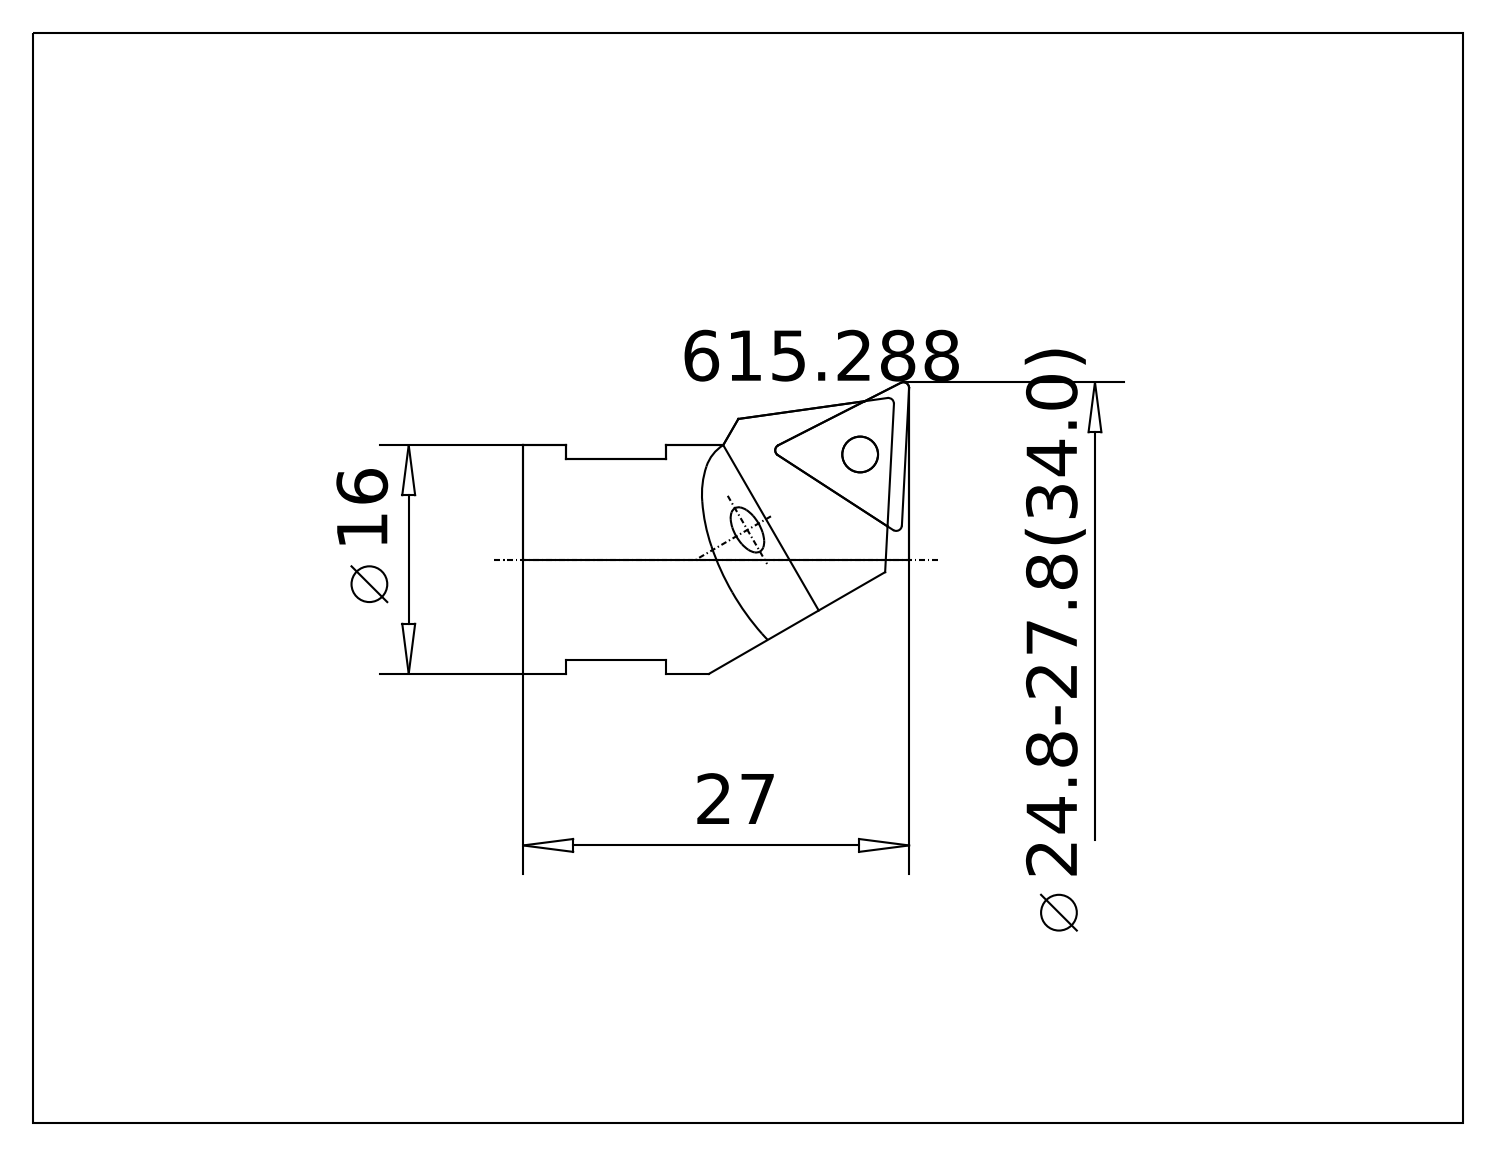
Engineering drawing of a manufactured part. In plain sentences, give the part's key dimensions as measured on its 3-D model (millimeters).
The part is named "615.288 Kaiser E25 TC11|655.383 Kaiser TCGT 110204 K10C;Kombinieren1; 615.288 Kaiser E25 TC11|694.122 Kaiser ETL M2.5x6.5 T7 IP 10S;Kreismuster1; 615.288 Kaiser E25 TC11|615.288 Kaiser E25 TC11;Schnitt-Rotation2". Its 3-D file was written by "ACIS (automotive_design)". It is 3 solids with 131 faces: 32 planar, 55 cylindrical and 44 other. Overall it measures 27 by 20.38 by 16 millimeters. Its volume is 3 669 cubic millimeters and its surface area 2 366 square millimeters. Round holes: 1 of diameter 2, 1 of diameter 2.5, 1 of diameter 2.8, 1 of diameter 3, 1 of diameter 8.5, 1 of diameter 10. Round bosses or shafts: 1 of diameter 16, 1 of diameter 3.45. Partial cylindrical surfaces (rounded edges, fillets, slot ends): 6 of radius 0.15, 6 of radius 0.4, 4 of radius 0.2, 2 of radius 3, 1 of radius 1.6, 1 of radius 6, 1 of radius 7.8. The main face-to-face distances are 6.1, 14, 8.48, 2.38, 8.2, 2.1, 11.01, 11, 1.01, 1.
